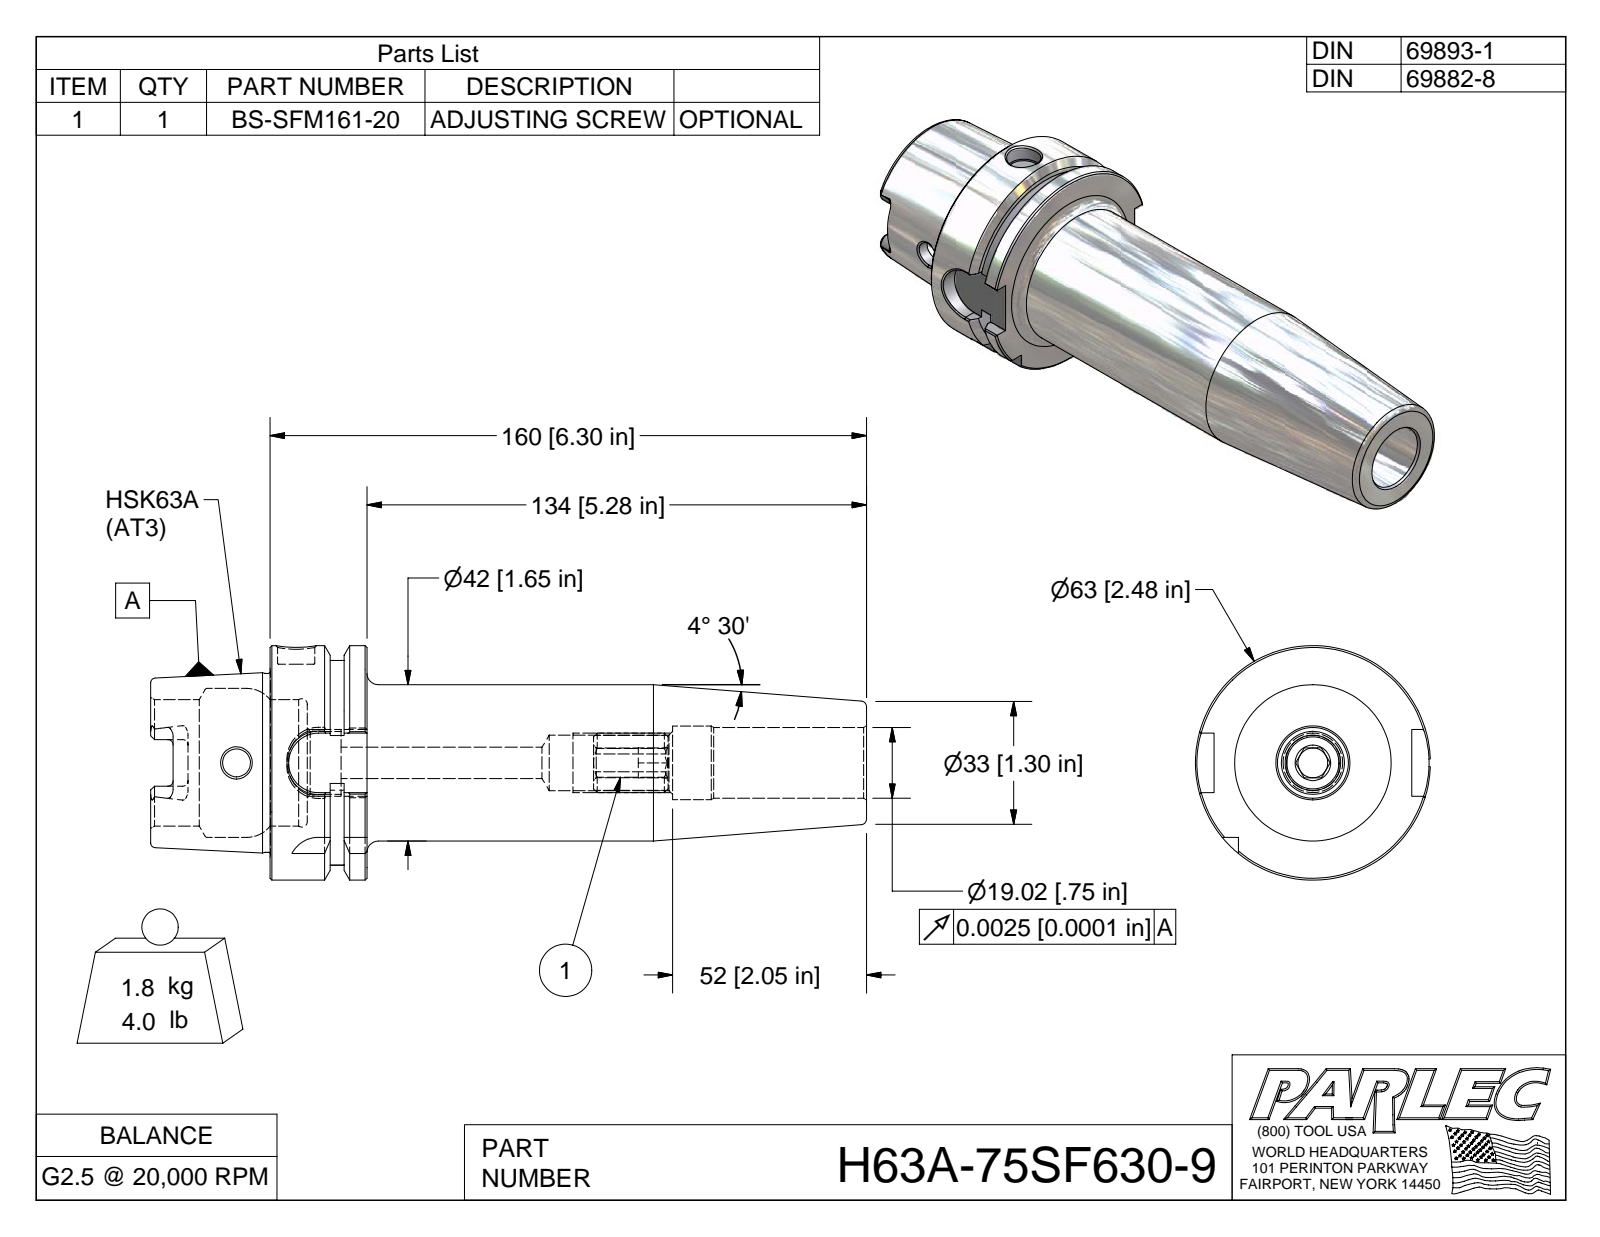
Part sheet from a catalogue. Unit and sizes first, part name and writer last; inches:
Units: inches
Overall size (bounding box): 7.559 × 2.48 × 2.48
Round holes (diameter × count): ⌀0.295 ×1, ⌀0.394 ×1, ⌀0.666 ×1, ⌀0.749 ×1, ⌀0.779 ×1, ⌀1.339 ×1, ⌀1.575 ×1
Round bosses / shafts (diameter × count): ⌀2.48 ×1, ⌀1.891 ×1, ⌀1.654 ×1
Partial cylindrical surfaces — rounded edges, fillets, slot ends (radius × count): R0.059 ×6, R0.315 ×5, R0.113 ×4, R1.083 ×1
Main face-to-face distances: 1.024, 0.241, 0.389, 0.394, 0.63, 5.276, 1.26, 6.299, 5.906, 1.654
Volume: 14.09 in³ · Surface area: 71.44 in²
Bodies: 2 solids, 157 faces (58 planar, 35 cylindrical, 64 other)
Part name (STEP PRODUCT): H63A-75SF630-9; H63A-75SF630-9-1; BS-SFM161-20
STEP written by: Autodesk Inventor 2009 (AUTOMOTIVE_DESIGN)
